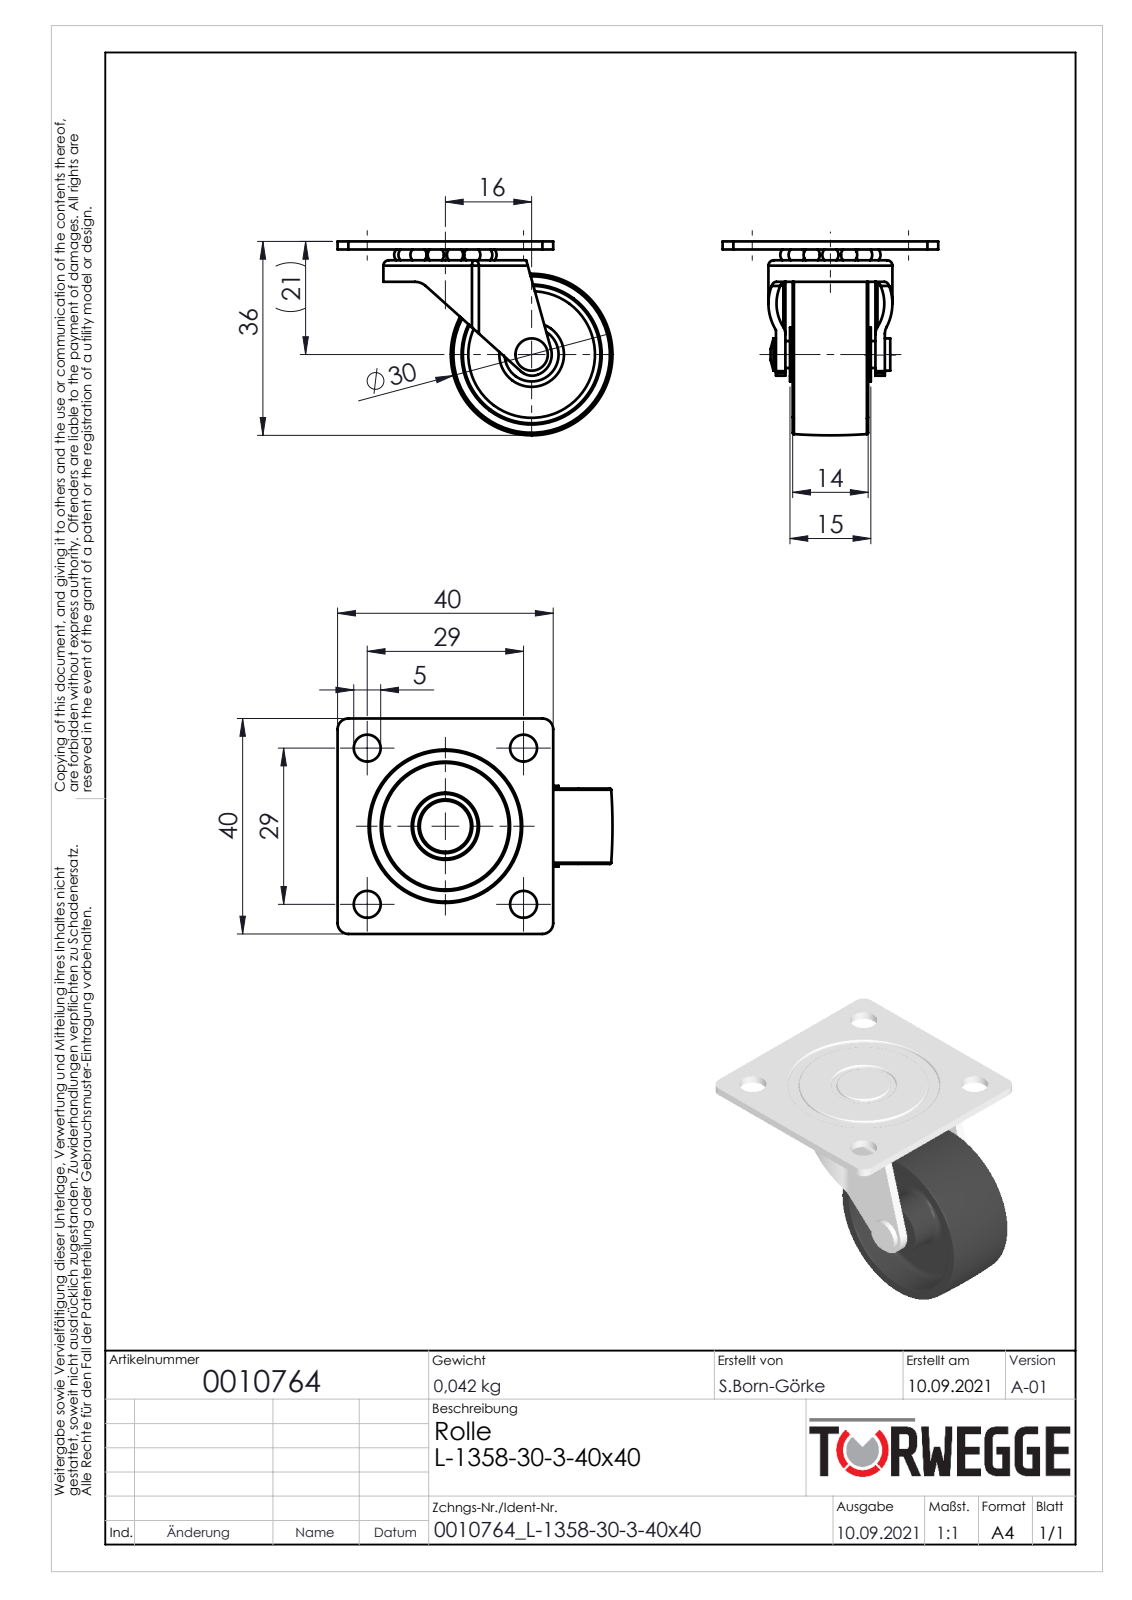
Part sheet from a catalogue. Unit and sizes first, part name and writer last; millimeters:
Units: millimetres
Overall size (bounding box): 51 × 40 × 36
Round holes (diameter × count): ⌀5 ×5, ⌀12 ×1, ⌀25.51 ×1, ⌀28 ×1
Round bosses / shafts (diameter × count): ⌀10 ×2, ⌀24 ×1, ⌀6 ×1
Partial cylindrical surfaces — rounded edges, fillets, slot ends (radius × count): R3 ×5, R2 ×4, R4 ×2, R10 ×1, R11.5 ×1
Main face-to-face distances: 1.5, 2, 5.5, 3, 4, 3.5, 8.6, 11.6, 1.75, 18.45
Hole centre spacings: 20.51, 29, 41.01
Volume: 9 630 mm³ · Surface area: 10 588 mm²
Bodies: 17 solids, 143 faces (28 planar, 53 cylindrical, 62 other)
Part name (STEP PRODUCT): 0010764
STEP written by: SolidWorks 2020 (AUTOMOTIVE_DESIGN)
